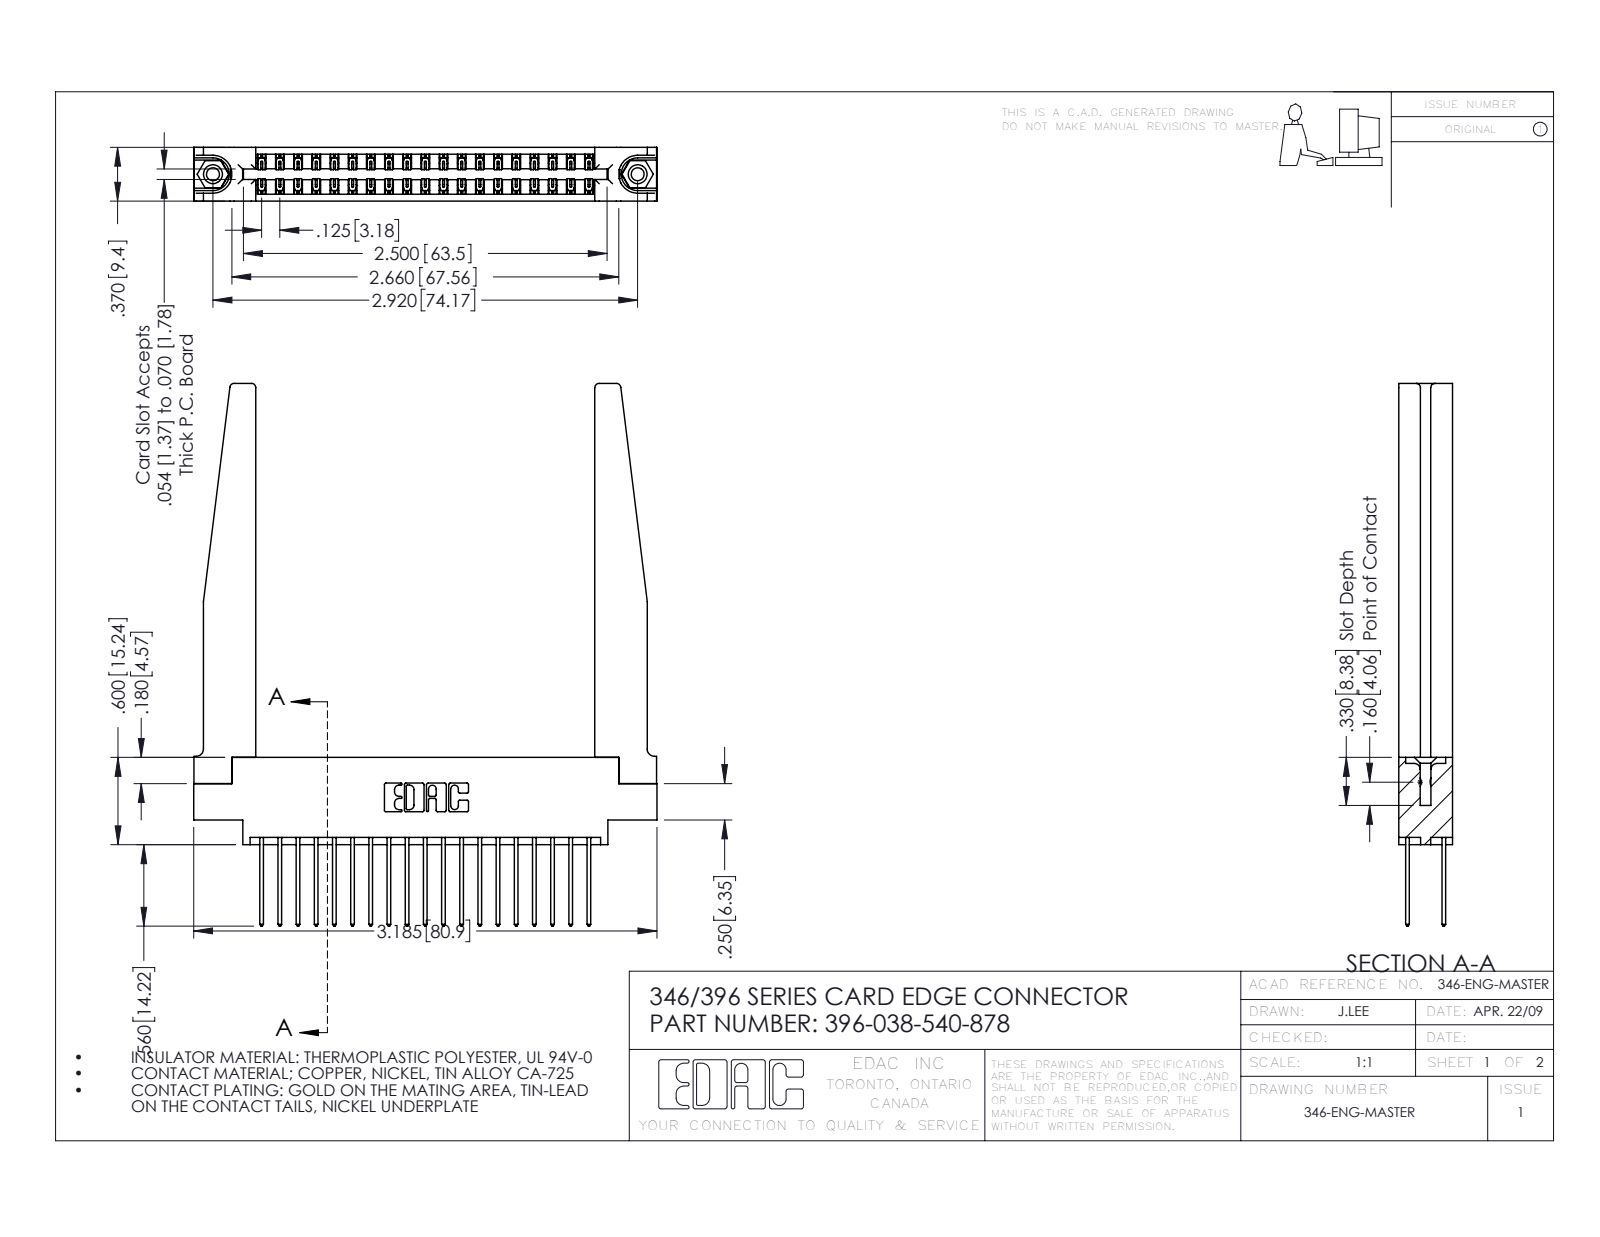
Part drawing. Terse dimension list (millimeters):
name: 346-220-078_345-220-078; 345-292-001_345-293-140; 345-250-001_345-250-001-102; 396-038-540-878 (+1 more)
written by: SolidWorks 2016 (CONFIG_CONTROL_DESIGN)
unit: mm
bodies: 43 solids, 2336 faces (1552 planar, 732 cylindrical, 52 other)
size: 94.7 × 80.9 × 9.4
volume: 14 600 mm³; area: 17 620 mm²
holes: 2× ⌀2.3, 2× ⌀3.2, 2× ⌀4, 1× ⌀1.6
bosses: 2× ⌀3.9
rounds: 57× R0.2, 38× R0.3, 22× R0.3, 8× R0.8, 6× R0.2, 6× R0.8, 3× R0.7, 2× R0.4
face distances: 9.4, 1.2, 8.2, 1.8, 6.4, 3.8, 3.8, 7.6, 0.6, 7
hole spacings: 6.2, 68.9, 74.2
